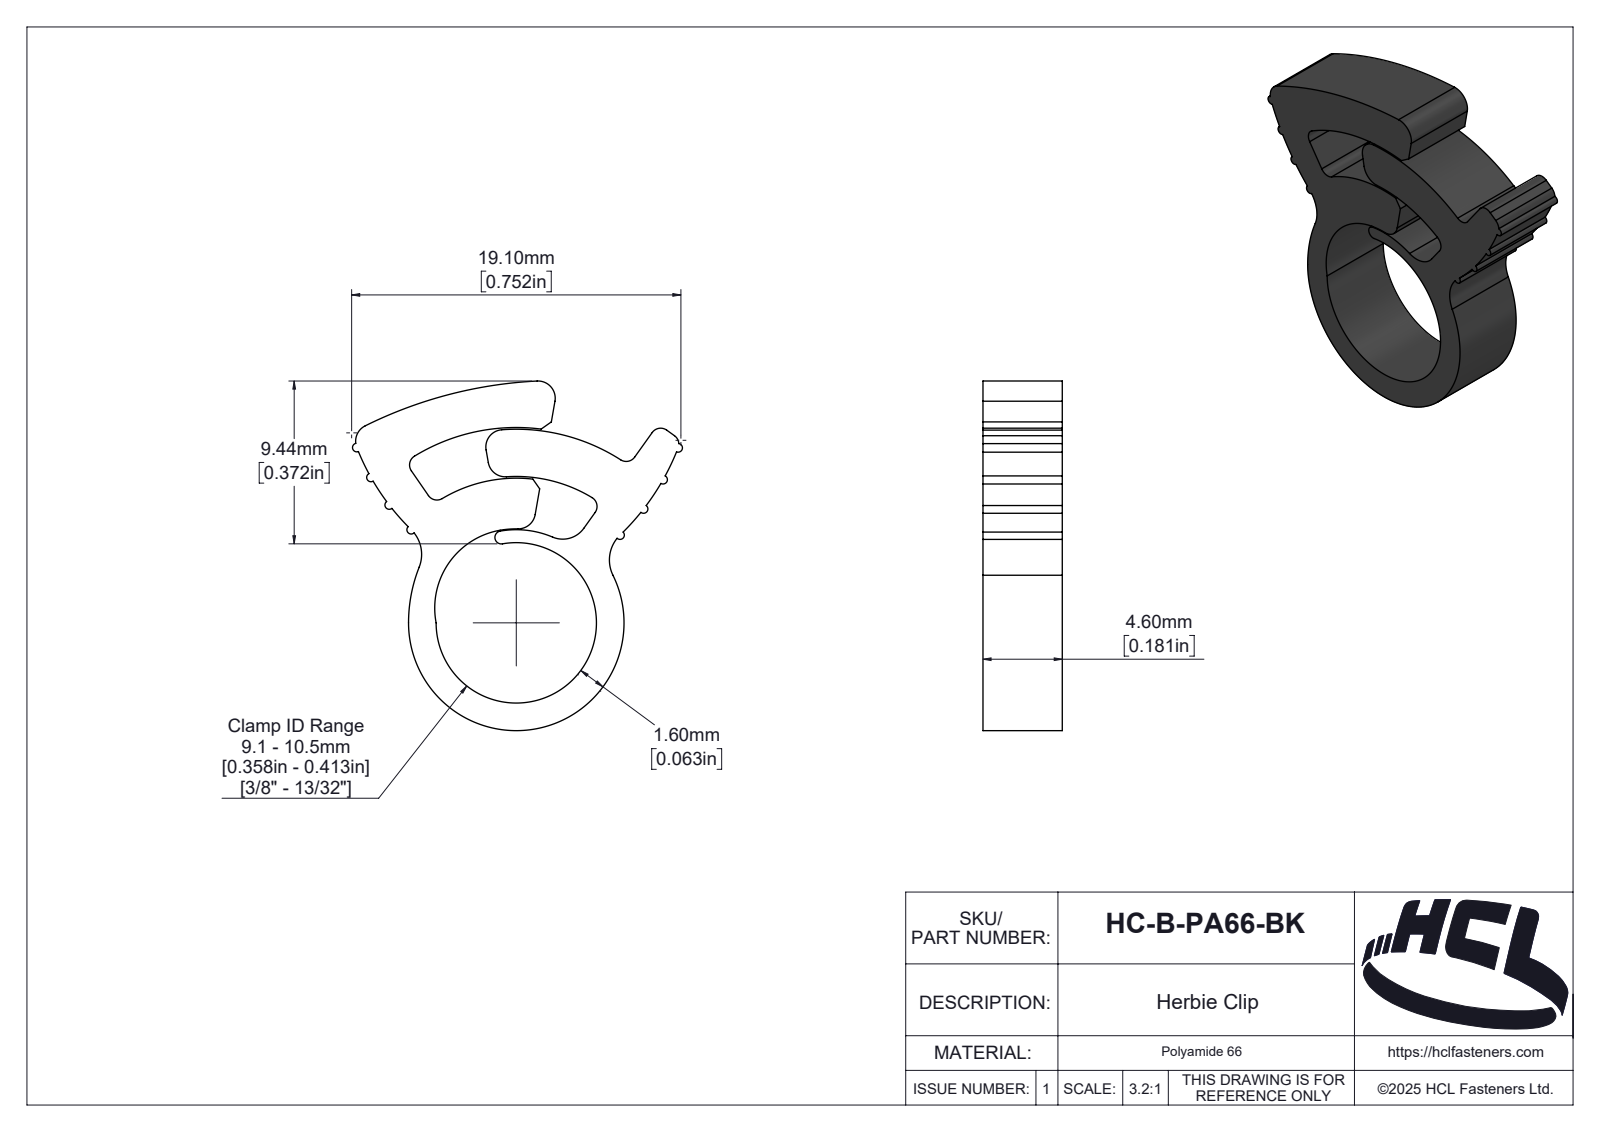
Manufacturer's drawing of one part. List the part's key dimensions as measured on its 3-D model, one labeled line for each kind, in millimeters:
Part name (STEP PRODUCT): HC-BB-PA66-BK
STEP written by: SolidWorks 2025 (AUTOMOTIVE_DESIGN)
Units: millimetres
Bodies: 1 solid, 162 faces (13 planar, 100 cylindrical, 49 other)
Overall size (bounding box): 23.17 × 22.52 × 5.1
Volume: 925 mm³ · Surface area: 1 207 mm²
Partial cylindrical surfaces — rounded edges, fillets, slot ends (radius × count): R0.25 ×8, R0.6 ×6, R1 ×5, R2 ×2, R0.17 ×1, R0.38 ×1, R0.67 ×1, R0.84 ×1
Main face-to-face distances: 5.1
